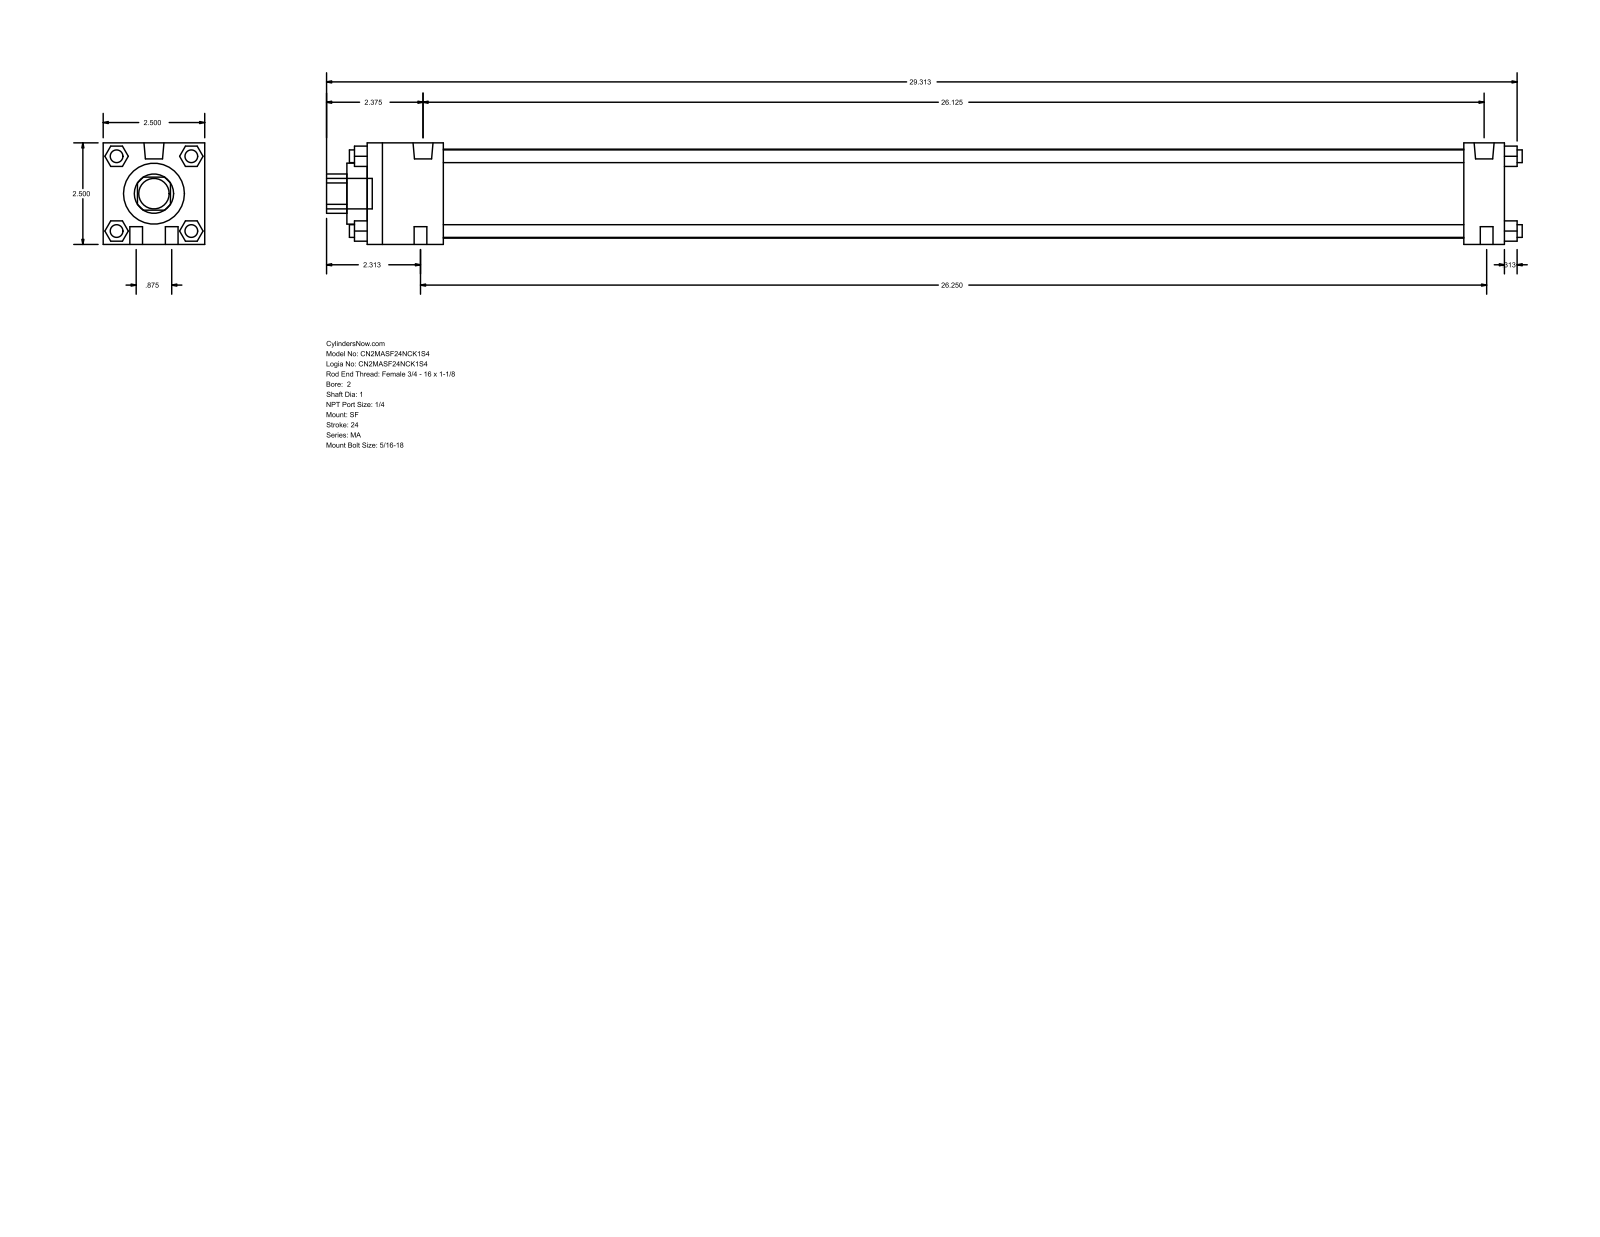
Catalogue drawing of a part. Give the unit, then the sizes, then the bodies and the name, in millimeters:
Units: millimetres
Overall size (bounding box): 747.71 × 63.5 × 63.5
Round holes (diameter × count): ⌀25.4 ×1, ⌀38.1 ×1, ⌀55.63 ×1
Round bosses / shafts (diameter × count): ⌀7.94 ×10, ⌀12.49 ×2, ⌀19.05 ×1
Partial cylindrical surfaces — rounded edges, fillets, slot ends (radius × count): R12.29 ×1
Main face-to-face distances: 63.5, 711.2, 12.7, 25.4, 685.8, 47.63, 638.17, 663.57, 23.37, 40.47
Bodies: 0 solids, 124 faces (94 planar, 30 cylindrical, 0 other)
Part name (STEP PRODUCT): MA_SF__0200_1
STEP written by: GSSL Pune (CONFIG_CONTROL_DESIGN)
